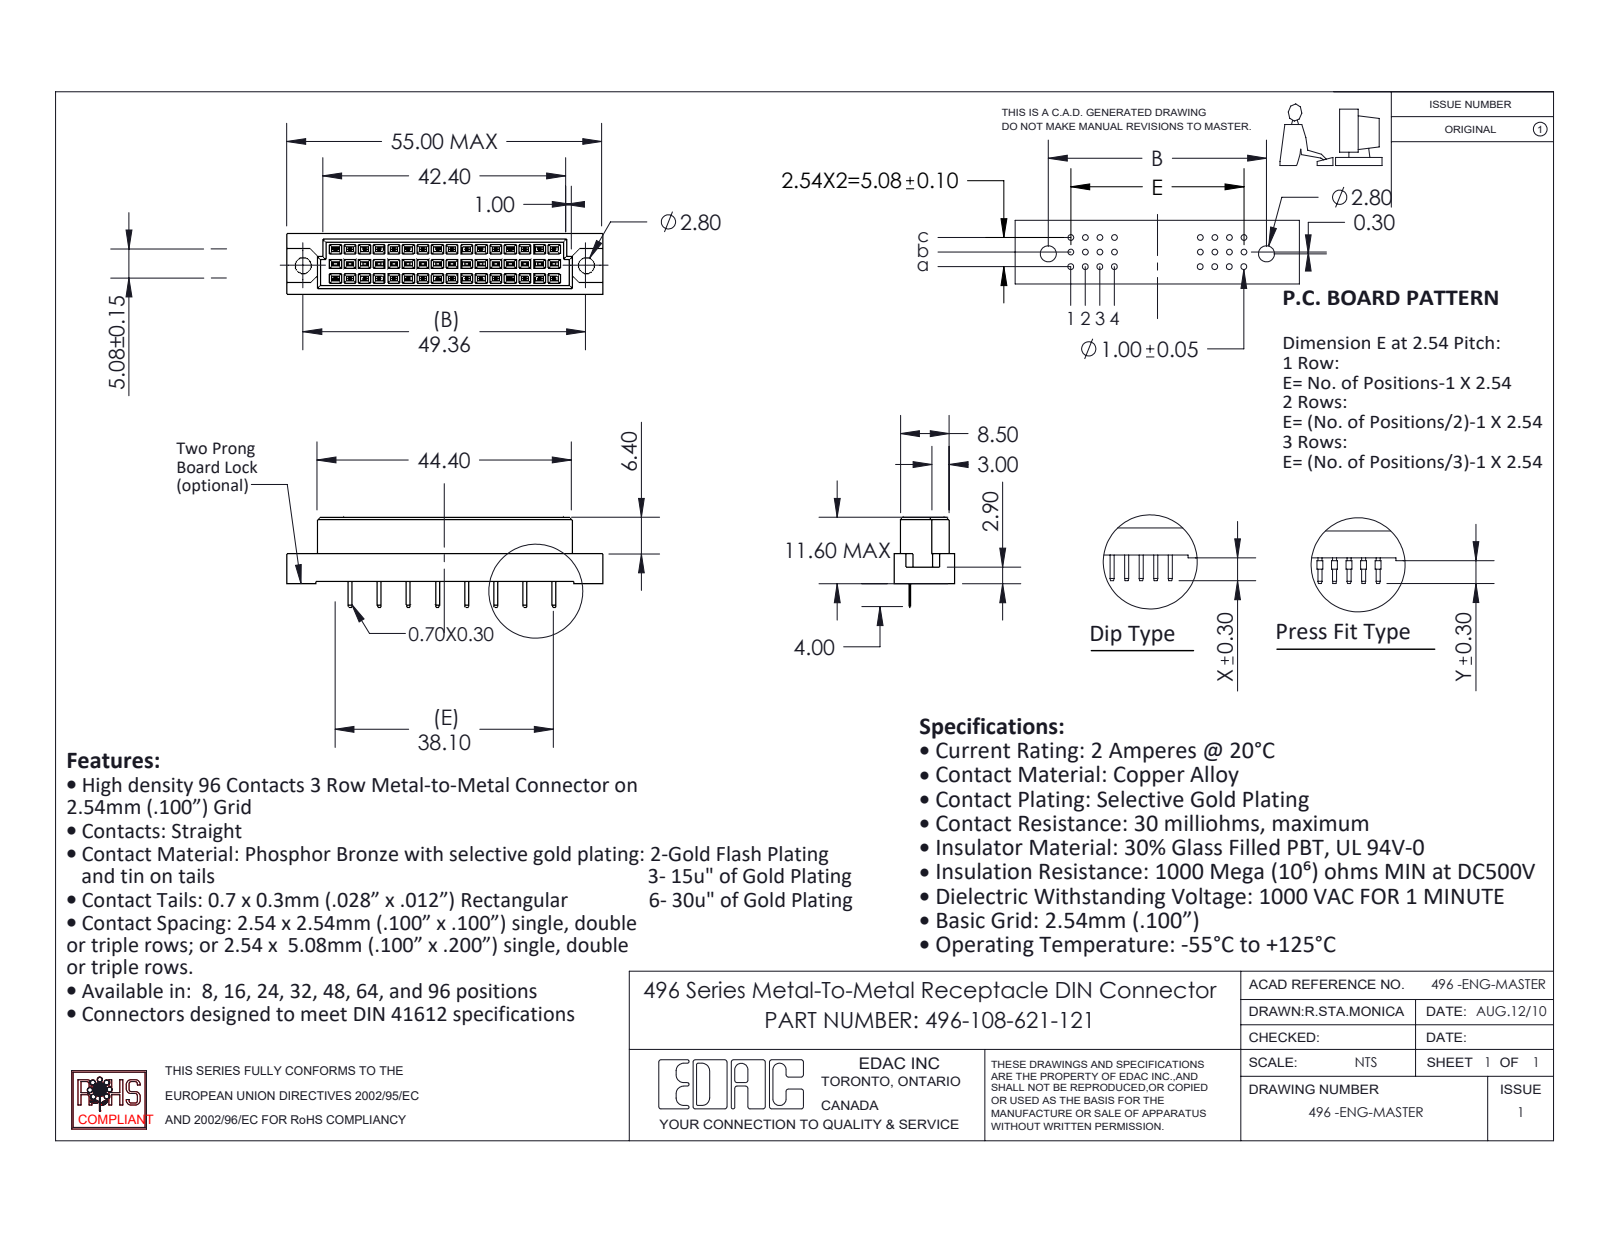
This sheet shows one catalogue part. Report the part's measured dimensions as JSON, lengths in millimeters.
{"part_name": "496 Part_48; 496-108-621-121; 496-290_21", "step_written_by": "SolidWorks 2020 (CONFIG_CONTROL_DESIGN)", "units": "millimeters", "bodies": {"solids": 9, "faces": 746, "planar": 742, "cylindrical": 4, "other": 0}, "overall_size": [55, 15.6, 10.6], "volume_mm3": 4604, "surface_area_mm2": 4357, "round_holes": [[2.8, 2]], "face_to_face_distances": [2.54, 5.08, 1.05, 9.55, 0.81, 10.6, 3.35, 1.73, 8.5, 0.56], "hole_center_spacings": [49.36]}
